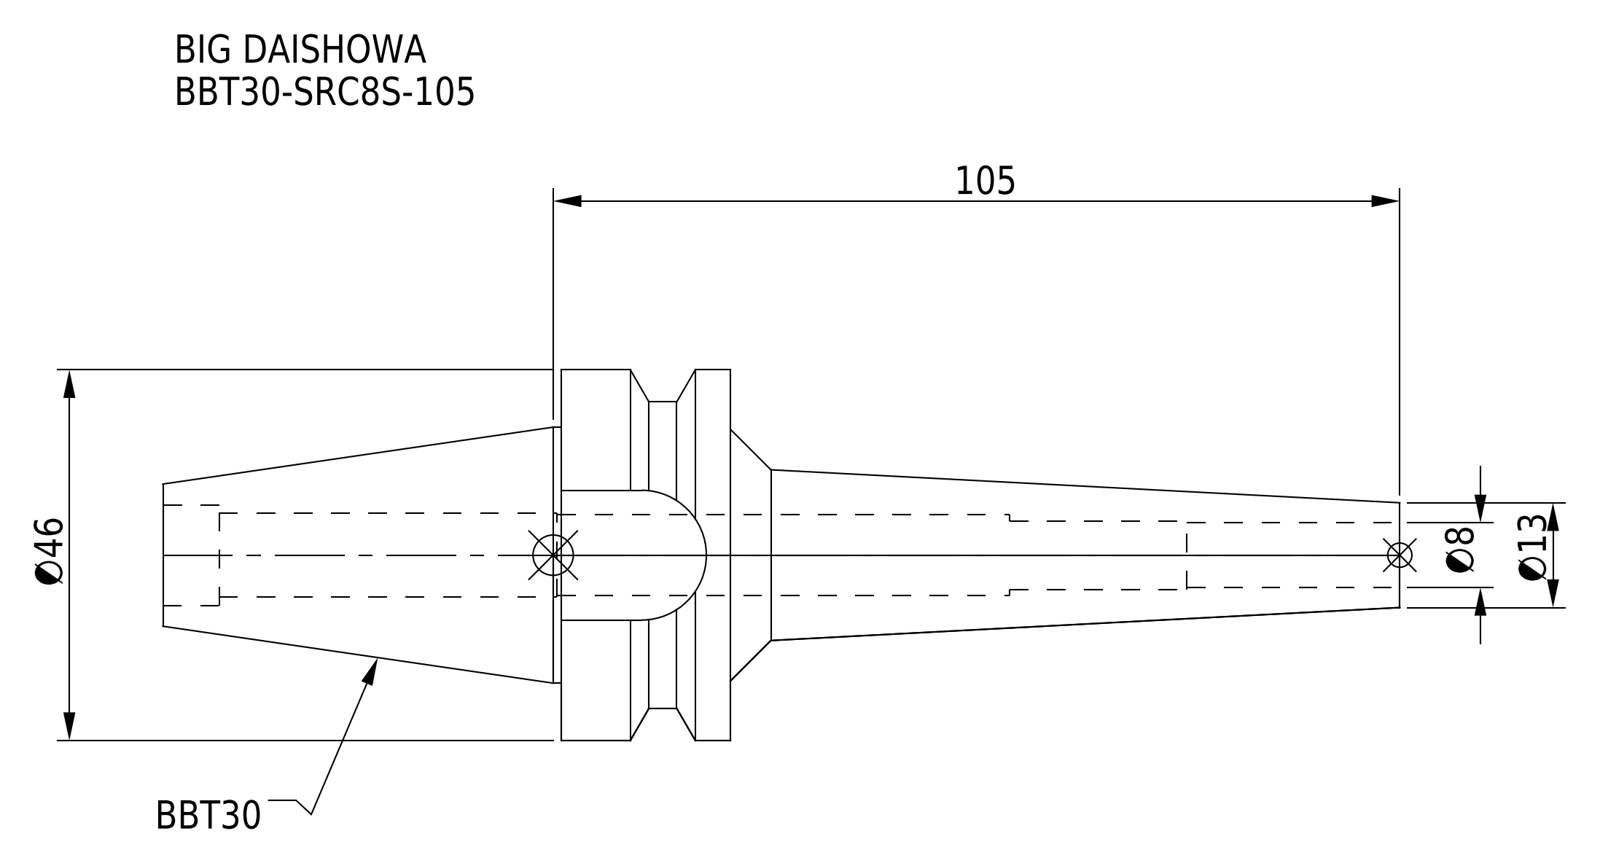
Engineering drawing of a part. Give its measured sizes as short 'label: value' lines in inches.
name: BBT30-SRC8S-105
written by: CREO PARAMETRIC BY PTC INC, 2016380 (AUTOMOTIVE_DESIGN)
unit: in
bodies: 1 solid, 46 faces (14 planar, 22 cylindrical, 10 other)
size: 6.039 × 1.811 × 1.811
volume: 3.868 in³; area: 29.34 in²
holes: 1× ⌀0.315, 1× ⌀0.335, 1× ⌀0.394, 1× ⌀0.409, 1× ⌀0.492
bosses: 1× ⌀1.811, 1× ⌀1.25
rounds: 1× R0.317, 1× R0.748
face distances: 0.827, 1.283, 2.772, 1.945, 0.634, 3.268, 4.094, 6.039, 5.764, 2.496
